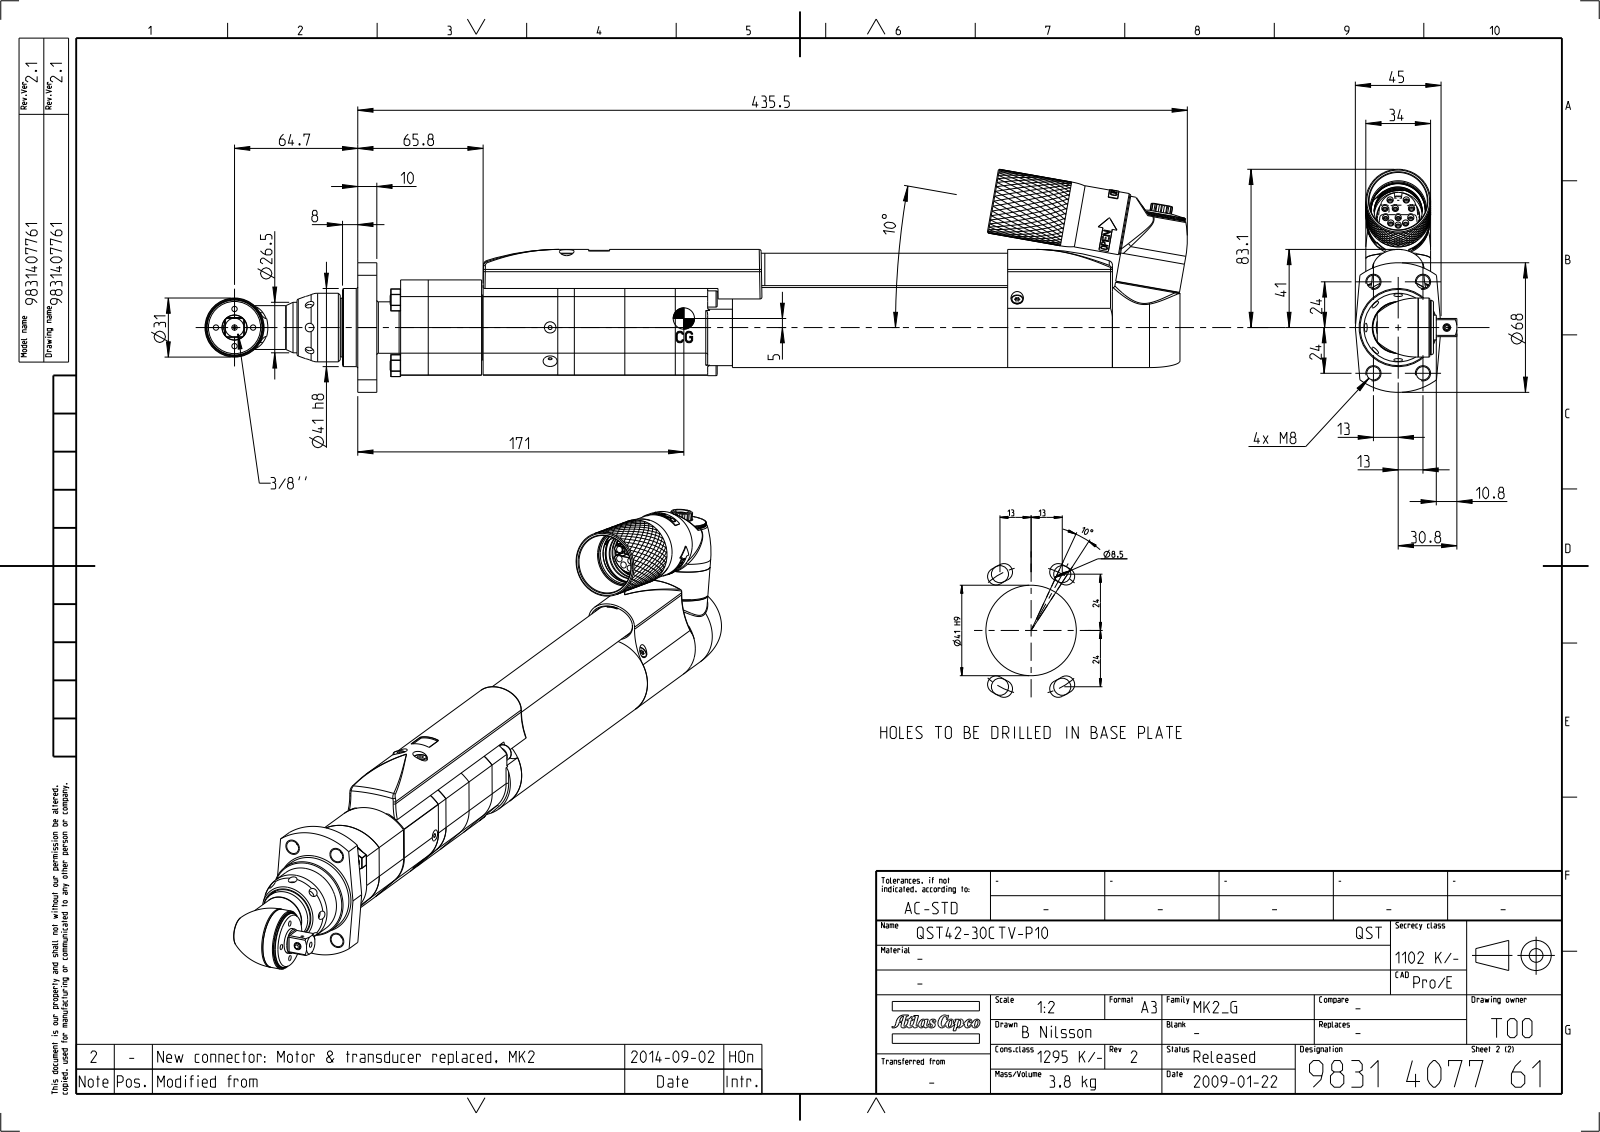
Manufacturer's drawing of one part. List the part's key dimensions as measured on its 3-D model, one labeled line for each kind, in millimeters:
Part name (STEP PRODUCT): 4230260102; 4230260112_ASM; 4230262500; 0219110017 (+8 more)
STEP written by: CREO PARAMETRIC BY PTC INC, 2015380 (CONFIG_CONTROL_DESIGN)
Units: millimetres
Bodies: 41 solids, 3647 faces (1414 planar, 1288 cylindrical, 945 other)
Overall size (bounding box): 515.71 × 117.06 × 53.3
Volume: 434 545 mm³ · Surface area: 261 280 mm²
Round holes (diameter × count): ⌀3.3 ×9, ⌀4.5 ×6, ⌀2.46 ×5, ⌀7 ×5, ⌀2.8 ×4, ⌀8 ×4, ⌀1.4 ×3, ⌀1.5 ×3, ⌀2.94 ×3, ⌀3.24 ×3, ⌀3.5 ×3, ⌀4.13 ×3
Round bosses / shafts (diameter × count): ⌀3 ×8, ⌀34 ×5, ⌀5 ×5, ⌀4 ×5, ⌀6 ×4, ⌀30 ×3, ⌀8.5 ×3, ⌀7 ×3
Partial cylindrical surfaces — rounded edges, fillets, slot ends (radius × count): R0.2 ×28, R0.5 ×21, R1 ×13, R1.5 ×6, R2 ×5, R5.25 ×4, R40 ×4, R6.5 ×3
Main face-to-face distances: 38, 26.5, 186.7, 3.5, 10, 27, 0.5, 113.7, 30, 140.2
Hole centre spacings: 15.92, 15, 9.22, 9.75, 13.6, 13.79, 15.26, 15.81
